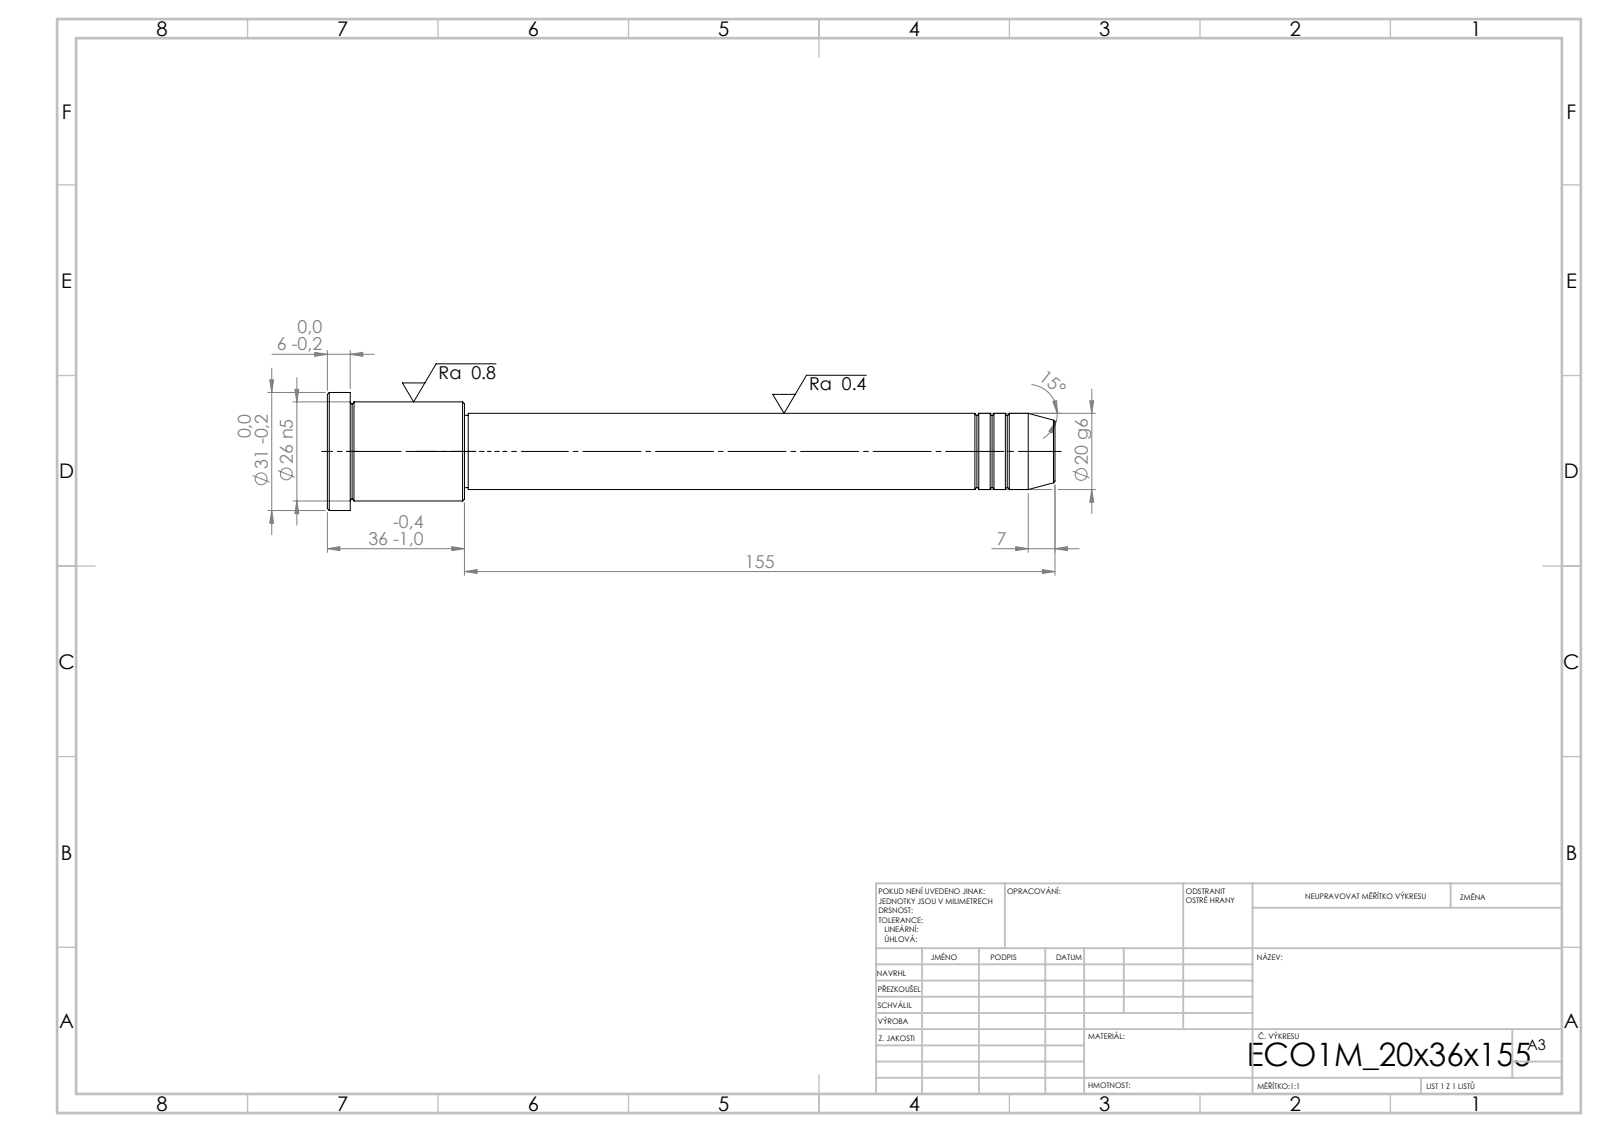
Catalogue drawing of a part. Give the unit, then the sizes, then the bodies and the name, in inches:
Units: inches
Overall size (bounding box): 7.52 × 1.22 × 1.22
Round bosses / shafts (diameter × count): ⌀1.22 ×1, ⌀1.024 ×1, ⌀0.787 ×1, ⌀0.748 ×1
Main face-to-face distances: 0.236, 1.181, 1.417, 6.102, 7.283, 7.52, 6.063, 0.039, 1.22, 1.457
Volume: 4.187 in³ · Surface area: 22.15 in²
Bodies: 1 solid, 43 faces (5 planar, 14 cylindrical, 24 other)
STEP written by: SolidWorks 2019 (CONFIG_CONTROL_DESIGN)
